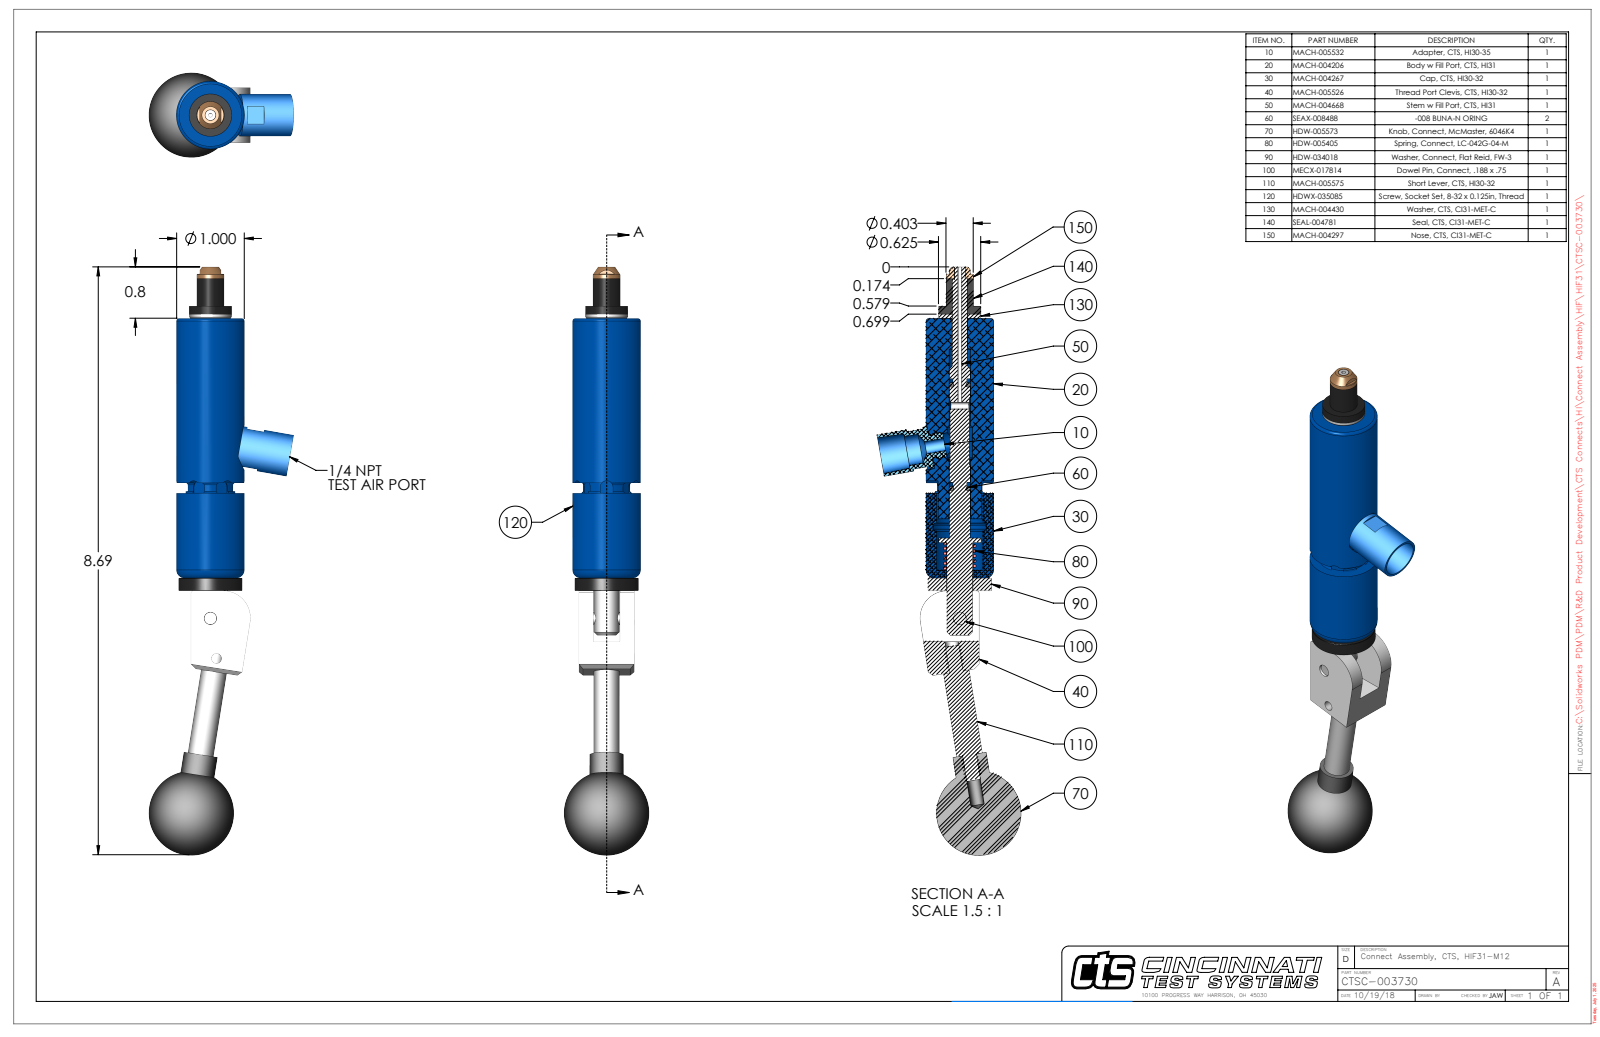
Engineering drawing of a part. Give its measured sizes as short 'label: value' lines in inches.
name: CTSC-003730
written by: SolidWorks 2023 (AUTOMOTIVE_DESIGN)
unit: in
bodies: 9 solids, 298 faces (113 planar, 120 cylindrical, 65 other)
size: 8.692 × 2.128 × 1.25
volume: 5.073 in³; area: 38.78 in²
holes: 2× ⌀0.201, 1× ⌀0.063, 1× ⌀0.109, 1× ⌀0.136, 1× ⌀0.15, 1× ⌀0.159, 1× ⌀0.187, 1× ⌀0.189, 1× ⌀0.218, 1× ⌀0.228, 1× ⌀0.229, 1× ⌀0.385
bosses: 1× ⌀1, 1× ⌀0.936, 1× ⌀0.625, 1× ⌀0.62, 1× ⌀0.5, 1× ⌀0.403, 1× ⌀0.38, 1× ⌀0.375
rounds: 6× R0.093, 2× R0.029, 1× R0.067, 1× R0.325, 1× R0.375, 1× R0.4, 1× R0.466
face distances: 0.21, 0.602, 0.812, 3.835, 4.023, 0.187, 0.391, 0.06, 3.896, 4.083
hole spacings: 0.599, 1.658, 2.252
